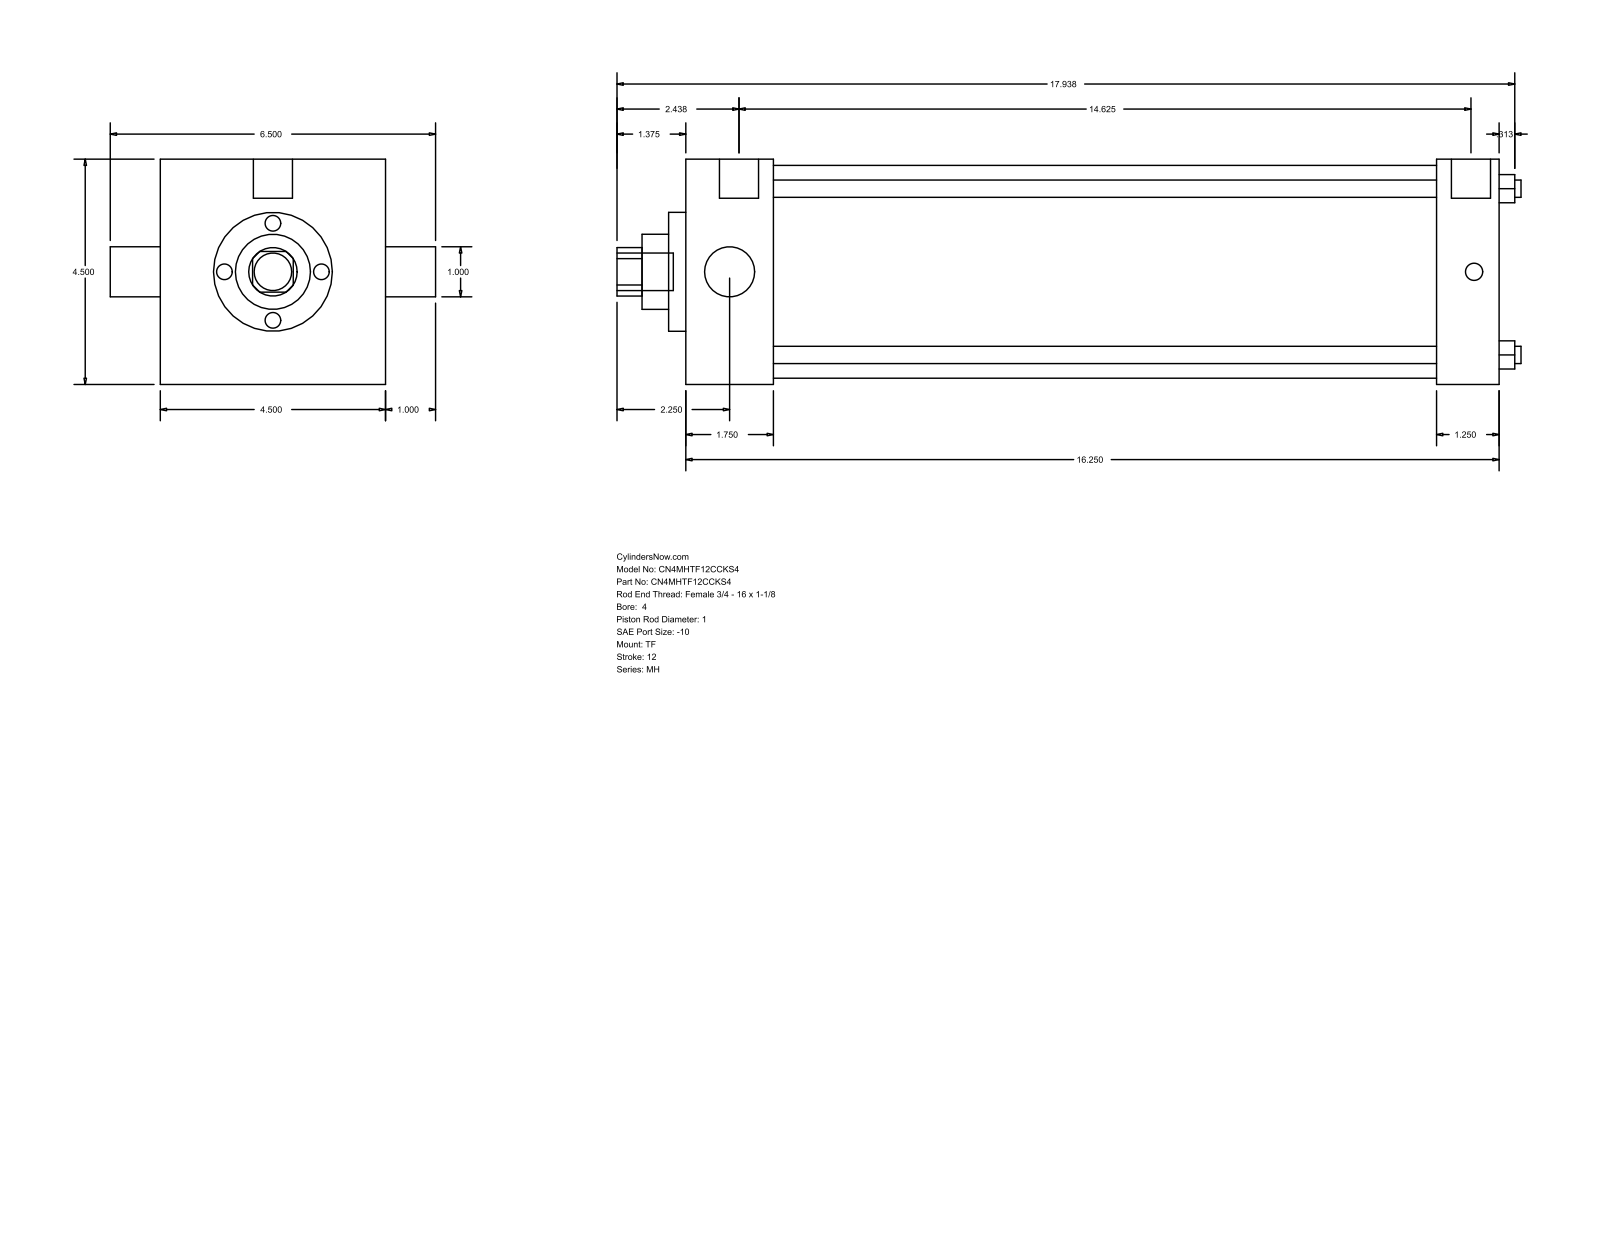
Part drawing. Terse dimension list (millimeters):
name: MH_TF__0400_1
written by: GSSL Pune (CONFIG_CONTROL_DESIGN)
unit: mm
bodies: 0 solids, 86 faces (61 planar, 25 cylindrical, 0 other)
size: 458.79 × 165.1 × 114.3
holes: 4× ⌀8.76, 2× ⌀25.4, 1× ⌀38.1, 1× ⌀60.33, 1× ⌀107.95
bosses: 3× ⌀8.73, 2× ⌀19.84, 1× ⌀19.05
rounds: 1× R12.29
face distances: 114.3, 412.76, 44.46, 368.3, 381.01, 336.55, 31.75, 8.73, 53.19, 389.74
hole spacings: 59.62, 84.32, 119.25
